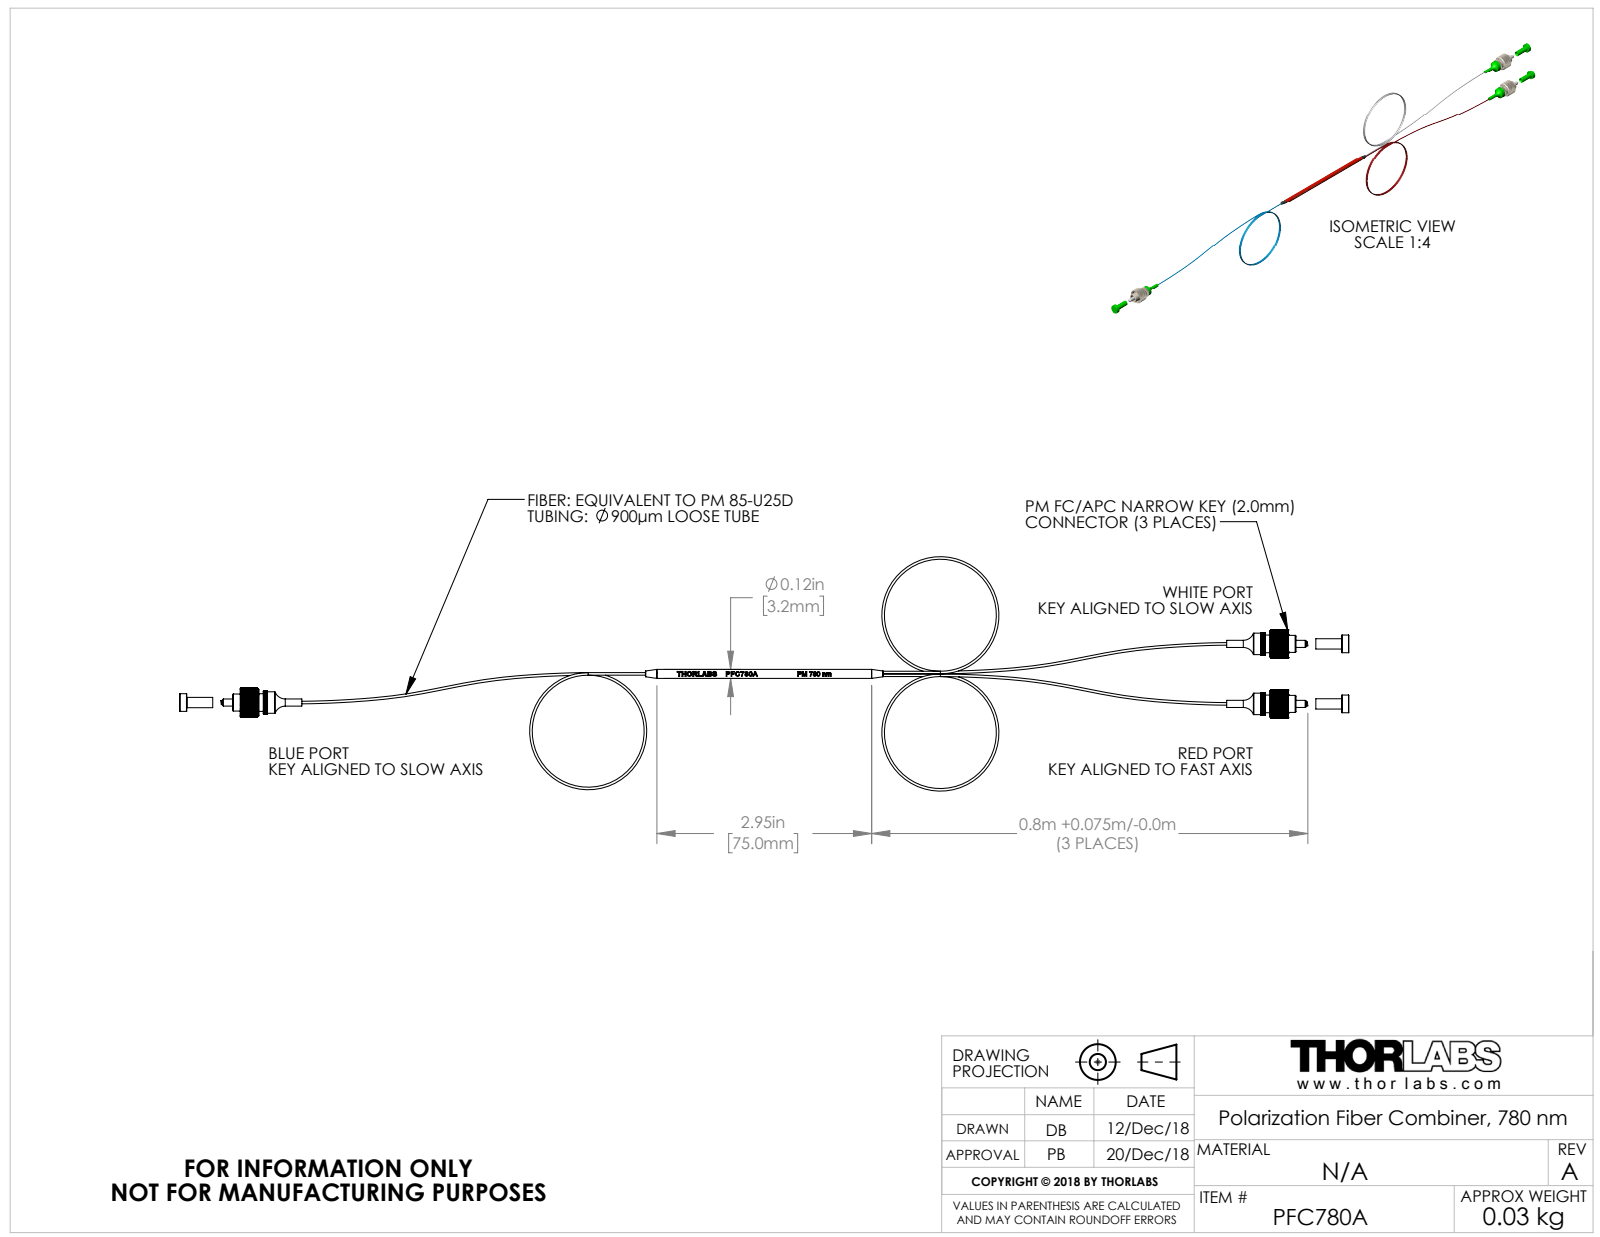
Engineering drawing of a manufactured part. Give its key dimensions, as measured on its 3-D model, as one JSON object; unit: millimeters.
{"part_name": "LA000PLBTTB; FC-APC Dust Cap_FC Dust Cap General; DWG1751_42-2mm; PANDA 850_60 (+8 more)", "step_written_by": "SolidWorks 2018 (CONFIG_CONTROL_DESIGN)", "units": "millimeters", "bodies": {"solids": 32, "faces": 2626, "planar": 1277, "cylindrical": 893, "other": 456}, "overall_size": [408.3, 81.85, 14.2], "volume_mm3": 3275, "surface_area_mm2": 13578, "round_holes": [[0.5, 6], [0.9, 3], [0.95, 3], [1, 3], [2.5, 3], [2.8, 3], [3.36, 3], [4.38, 3], [4.4, 3], [5.08, 3], [5.55, 3], [6.1, 3]], "round_bosses_or_shafts": [[7.5, 3], [7.07, 3], [6.17, 3], [6.08, 3], [5.95, 3], [5.38, 3], [4.85, 3], [3.6, 3]], "partial_cylinders_radius": [[0.5, 6], [0.75, 3], [1.55, 3], [2.26, 3], [3.98, 3], [5, 3], [0.45, 2], [1, 1]], "face_to_face_distances": [6.86, 6.85, 2, 1.43, 4.97, 2.97, 349.97, 1.54, 3.43, 27.68], "hole_center_spacings": [10.2, 0.47, 0.48, 0.95, 4.03, 9.74, 10.24, 10.66]}
